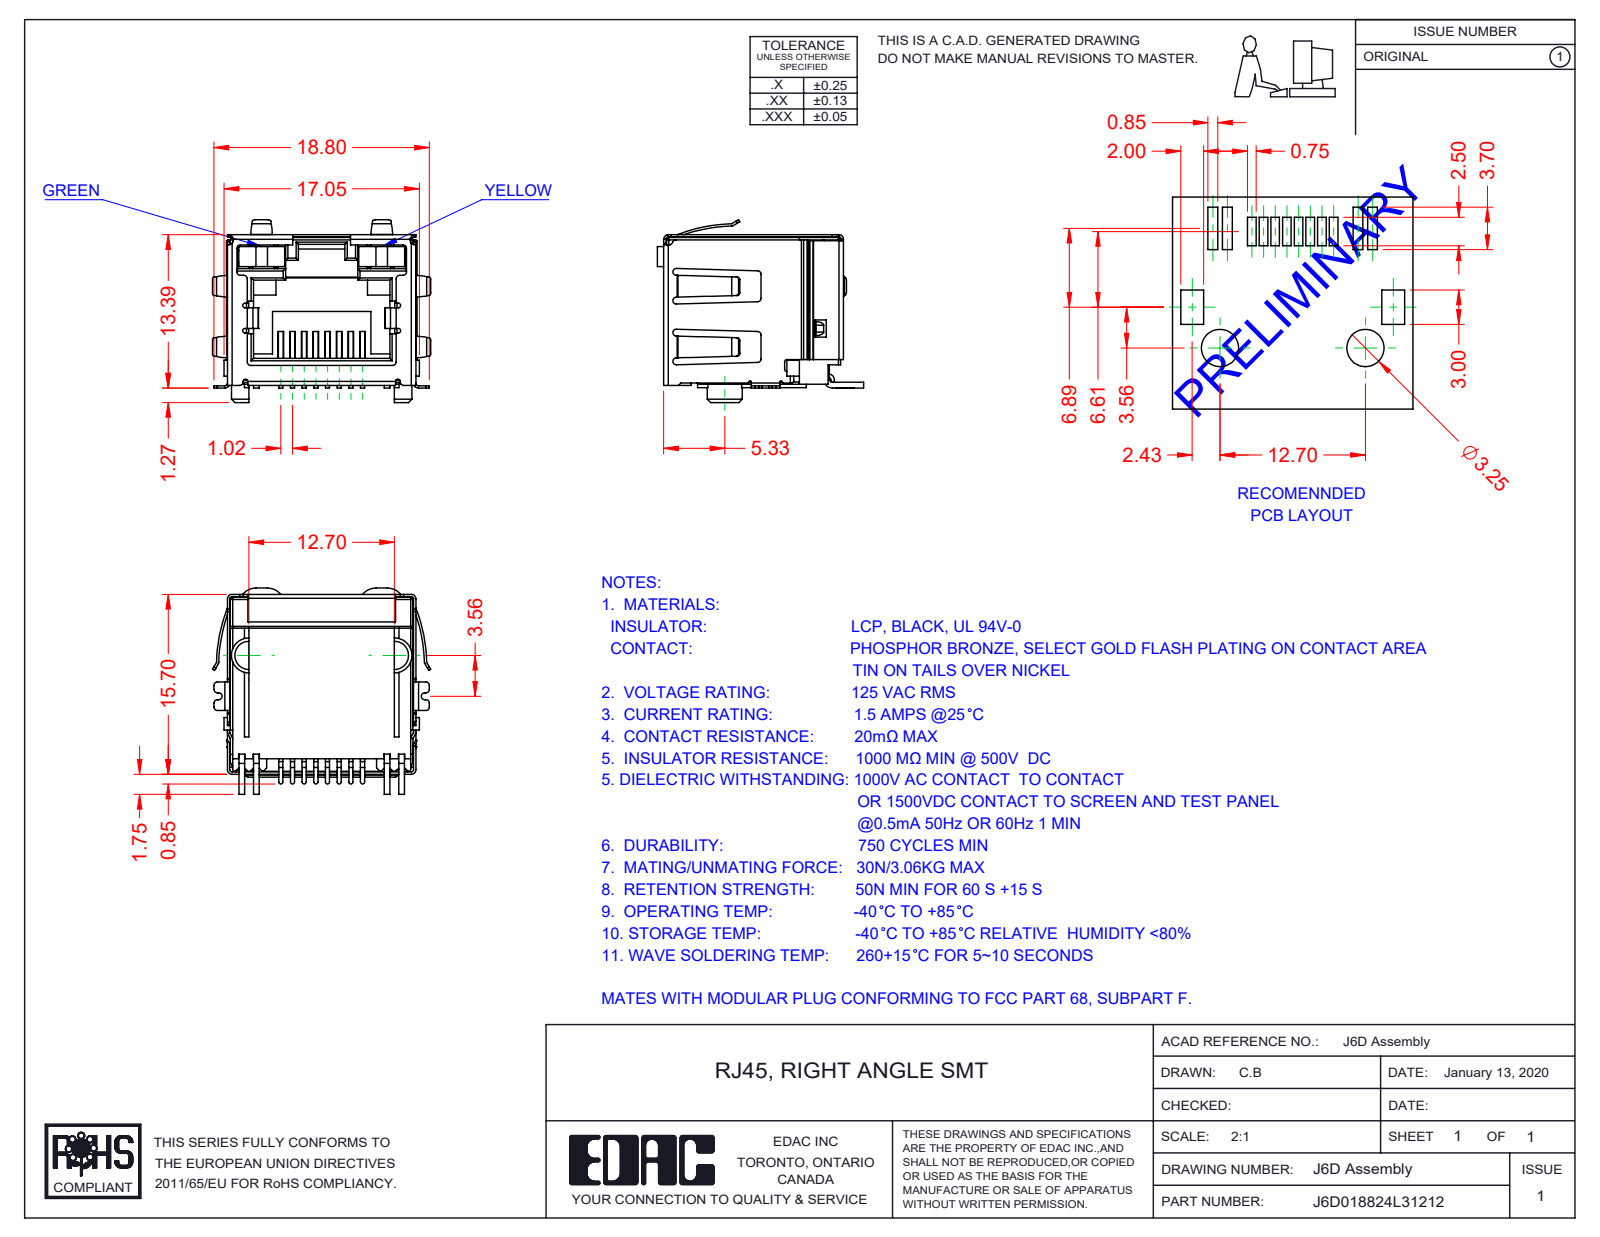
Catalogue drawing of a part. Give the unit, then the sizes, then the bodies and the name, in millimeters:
Units: millimetres
Overall size (bounding box): 19.06 × 18 × 15.95
Partial cylindrical surfaces — rounded edges, fillets, slot ends (radius × count): R0.3 ×55, R0.2 ×40, R0.4 ×19, R0.25 ×16, R0.1 ×12, R0.15 ×8, R0.18 ×8, R0.5 ×6
Main face-to-face distances: 16, 16.2, 16.25, 2.25, 1, 15.95, 12.8, 0.45, 13.05, 10.6
Volume: 1 790 mm³ · Surface area: 4 796 mm²
Bodies: 12 solids, 1028 faces (701 planar, 282 cylindrical, 45 other)
Part name (STEP PRODUCT): 6D Contacts; J6D018824L31212; 6D Shield_LED - EMI; 6D LED LH_3-Green (+2 more)
STEP written by: SolidWorks 2016 (CONFIG_CONTROL_DESIGN)
